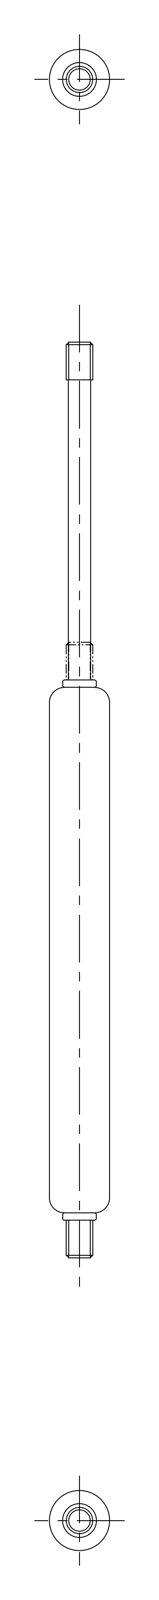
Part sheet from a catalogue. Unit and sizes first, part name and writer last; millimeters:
Units: millimetres
Overall size (bounding box): 122 × 8 × 8
Volume: 3 897 mm³ · Surface area: 2 363 mm²
Bodies: 2 solids, 36 faces (0 planar, 0 cylindrical, 36 other)
Part name (STEP PRODUCT): rod; TM_276_40_30_28670_36
STEP written by: CADfix (AUTOMOTIVE_DESIGN)
